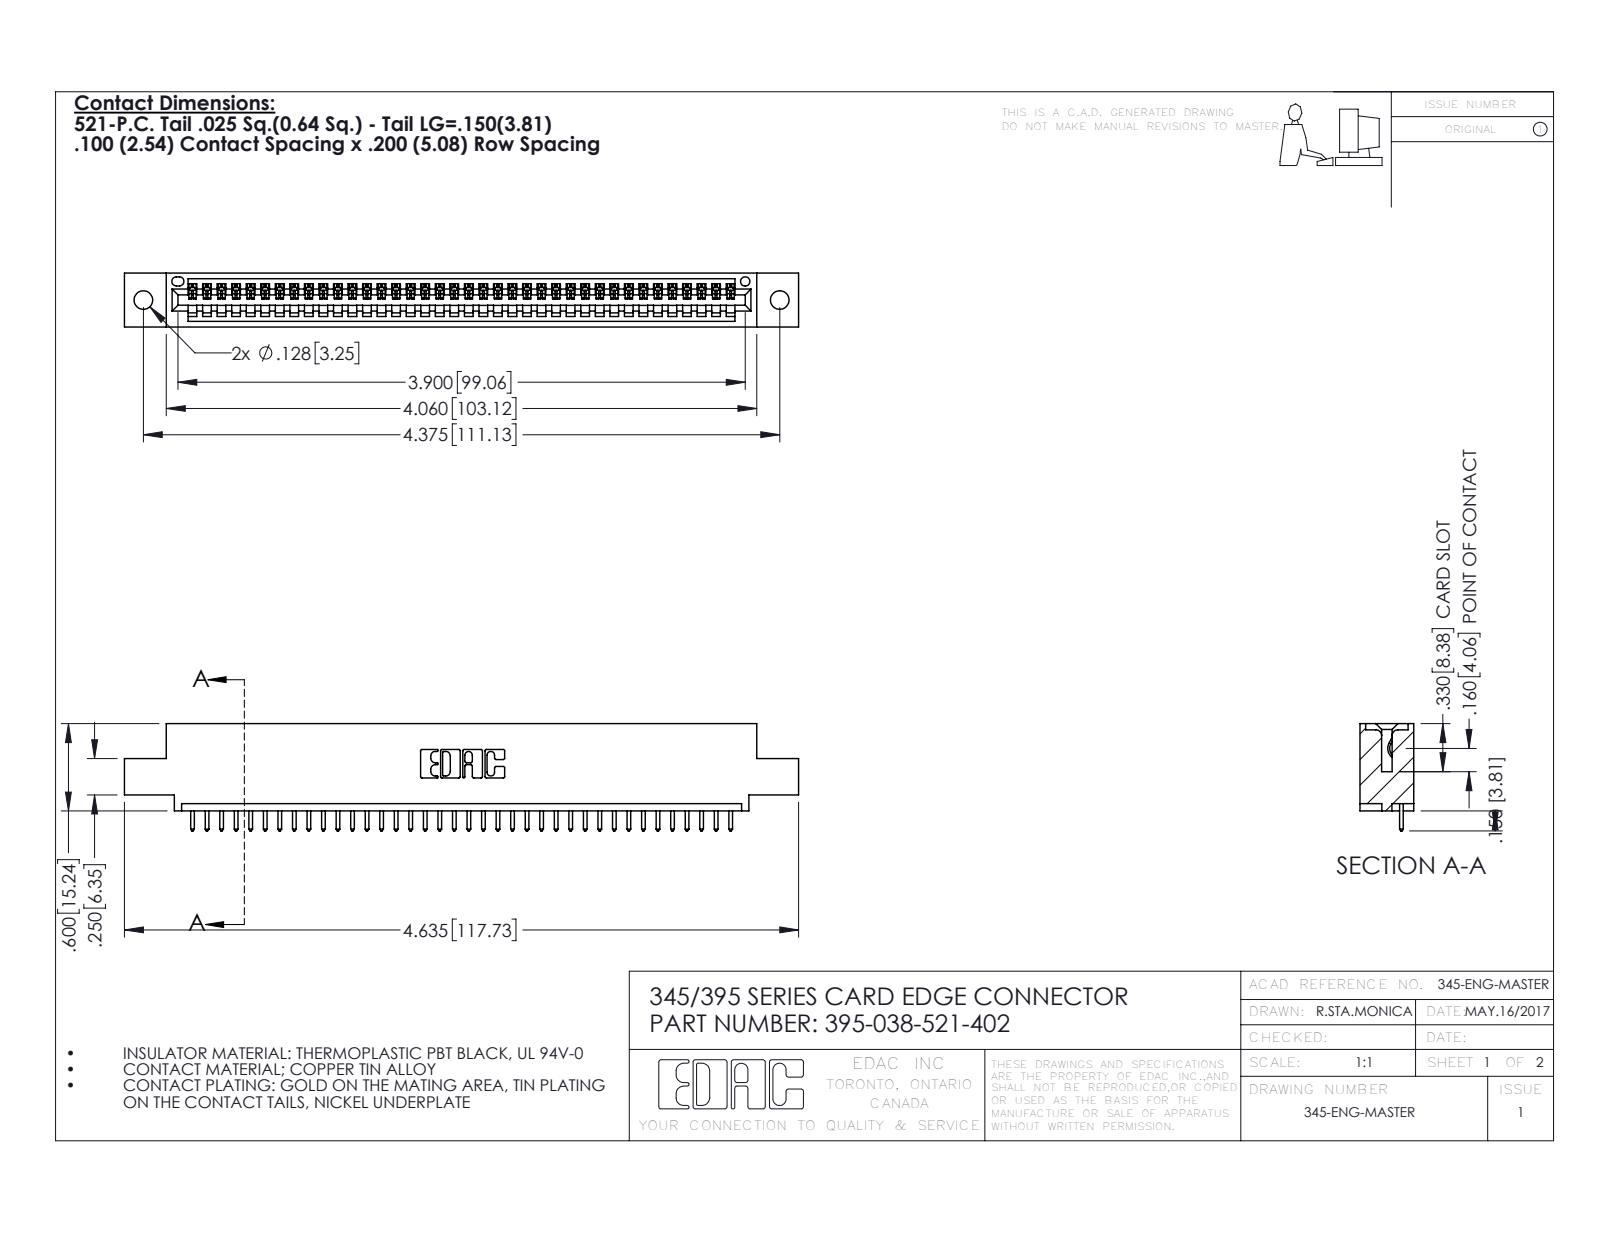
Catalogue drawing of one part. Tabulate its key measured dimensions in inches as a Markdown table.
| quantity | value |
| --- | --- |
| part name | 395-038-521-402; 345 Part_0.110 Offset - 0.128 Dia; 345-292-001_345-293-121 |
| STEP written by | SolidWorks 2016 (CONFIG_CONTROL_DESIGN) |
| units | inches |
| bodies | 39 solids, 2334 faces (1604 planar, 730 cylindrical, 0 other) |
| overall size | 4.635 × 0.737 × 0.37 |
| volume | 0.667 in³ |
| surface area | 21.48 in² |
| round holes (diameter × count) | 0.128 × 2, 0.064 × 1 |
| partial cylindrical surfaces (radius × count) | 0.006 × 76, 0.01 × 76, 0.01 × 22, 0.007 × 6, 0.031 × 6, 0.026 × 3, 0.031 × 2, 0.04 × 2 |
| main face-to-face distances | 0.072, 0.298, 0.37, 0.2, 0.098, 0.272, 0.025, 0.225, 0.149, 0.072 |
| hole center spacings | 0.27, 4.139, 4.375 |
